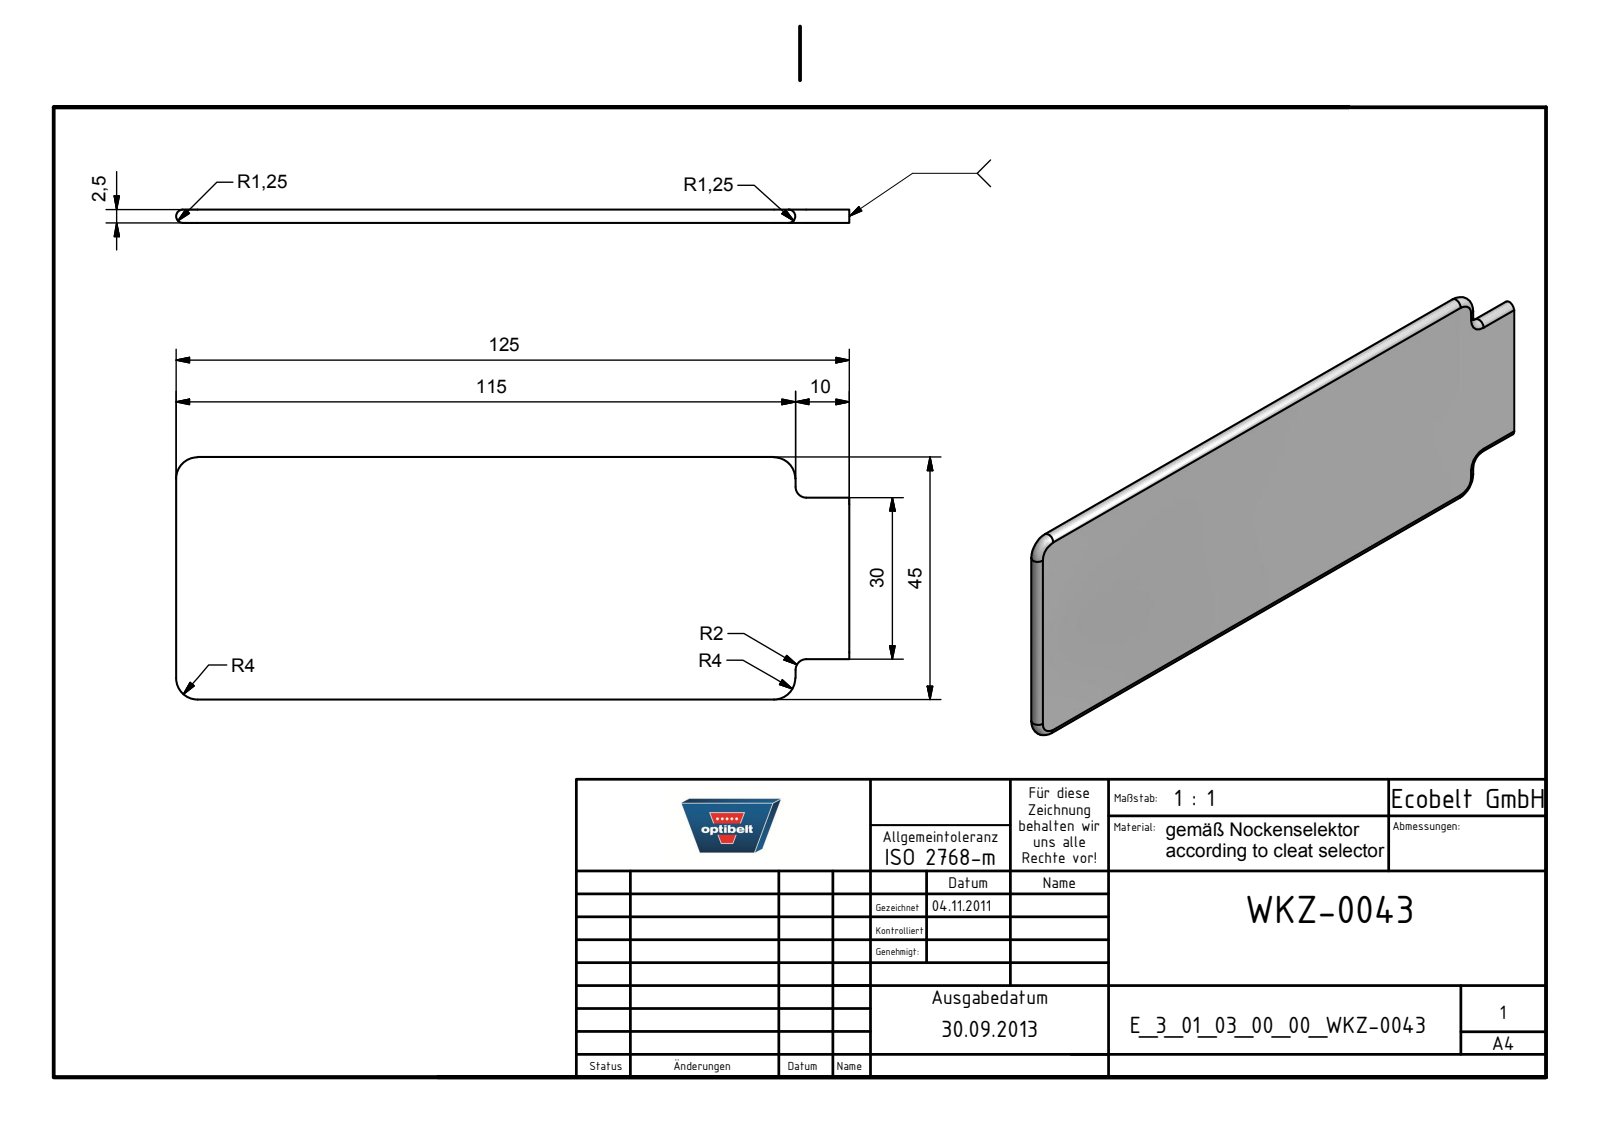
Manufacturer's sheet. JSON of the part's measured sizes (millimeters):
{"part_name": "E_3_01_03_00_00_WKZ-0043", "step_written_by": "Autodesk Inventor 2021 (AUTOMOTIVE_DESIGN)", "units": "millimeters", "bodies": {"solids": 1, "faces": 16, "planar": 3, "cylindrical": 7, "other": 6}, "overall_size": [125, 45, 2.5], "volume_mm3": 13456, "surface_area_mm2": 11429, "partial_cylinders_radius": [[1.25, 6]], "face_to_face_distances": [2.5]}
